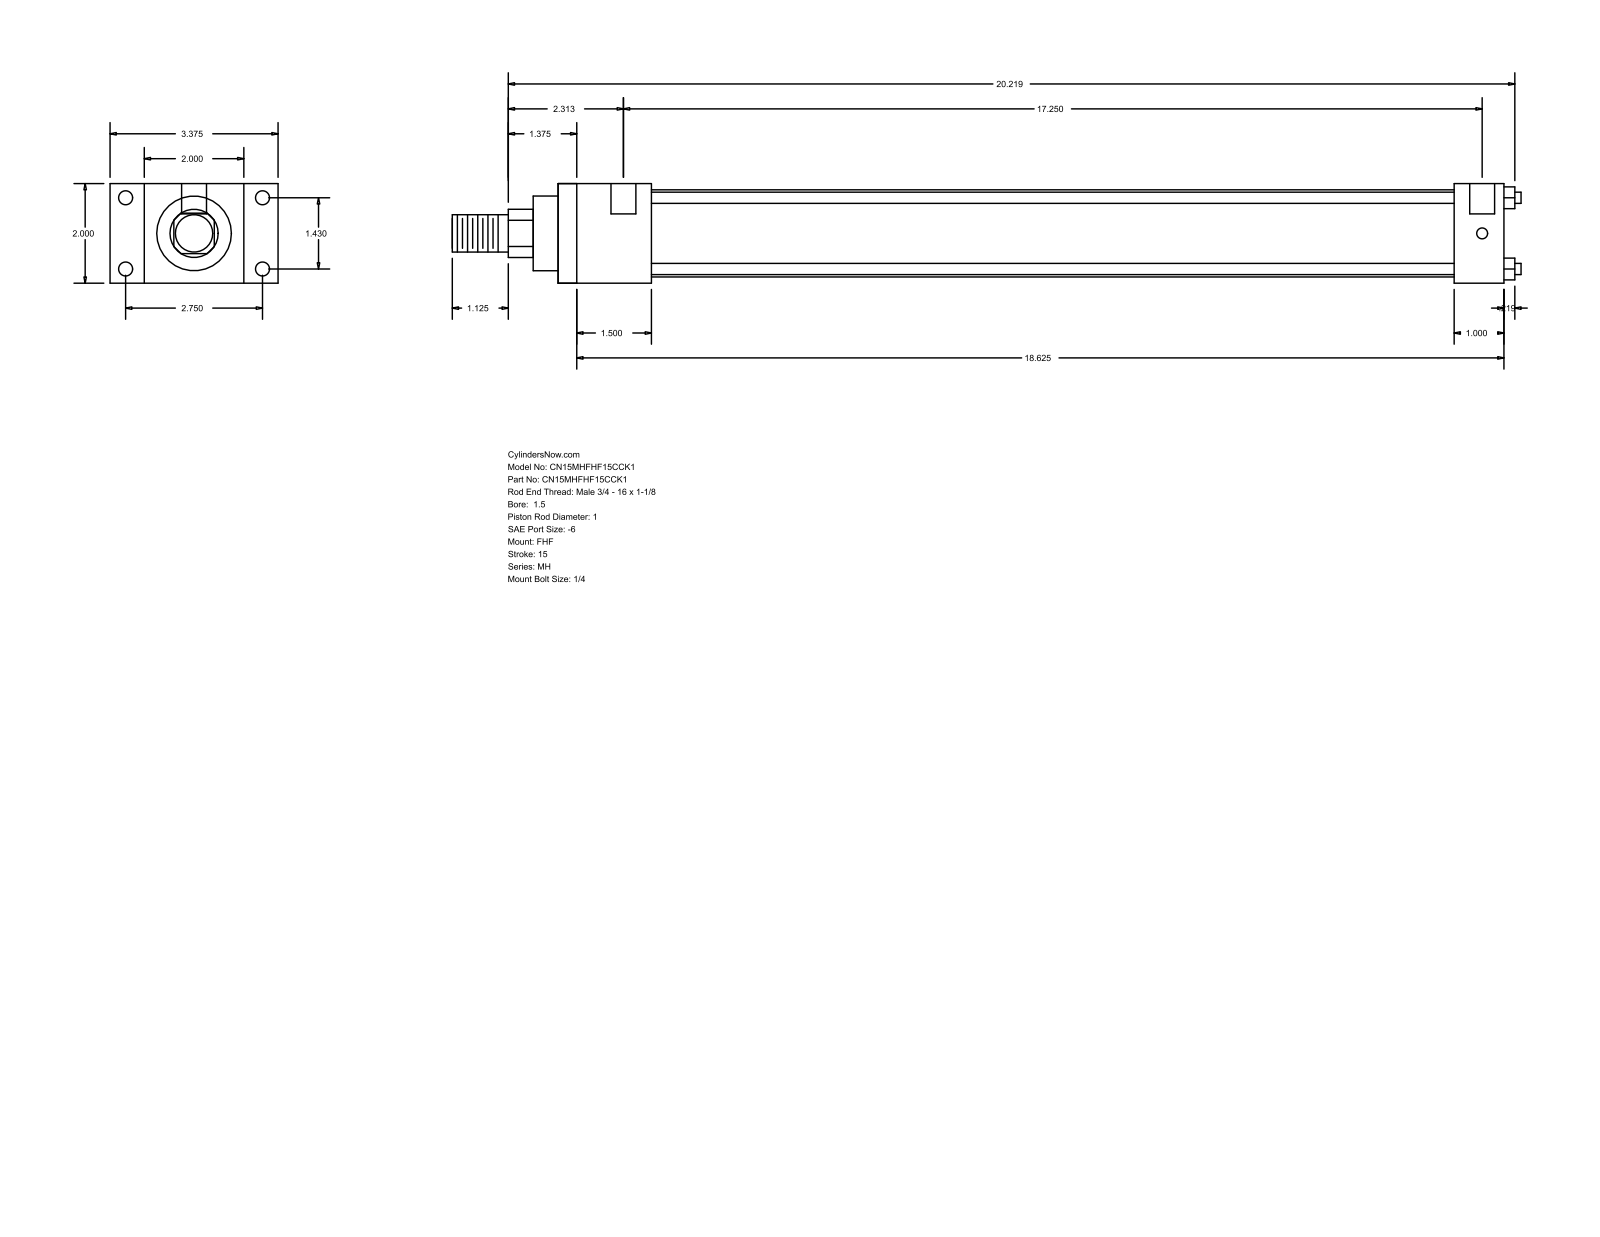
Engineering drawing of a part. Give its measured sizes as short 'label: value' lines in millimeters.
name: MH_FHF__0150_1
written by: GSSL Pune (CONFIG_CONTROL_DESIGN)
unit: mm
bodies: 0 solids, 88 faces (60 planar, 28 cylindrical, 0 other)
size: 545.31 × 85.72 × 50.8
holes: 4× ⌀5.56, 4× ⌀7.14, 2× ⌀12.7
bosses: 4× ⌀5.71, 1× ⌀44.45, 1× ⌀38.1, 1× ⌀25.4, 1× ⌀19.05
rounds: 1× R12.29
face distances: 50.8, 17.46, 68.26, 47.63, 85.72, 482.6, 434.97, 25.4, 457.2, 409.57
hole spacings: 36.32, 69.84, 78.72, 441.33, 3.18, 438.15
